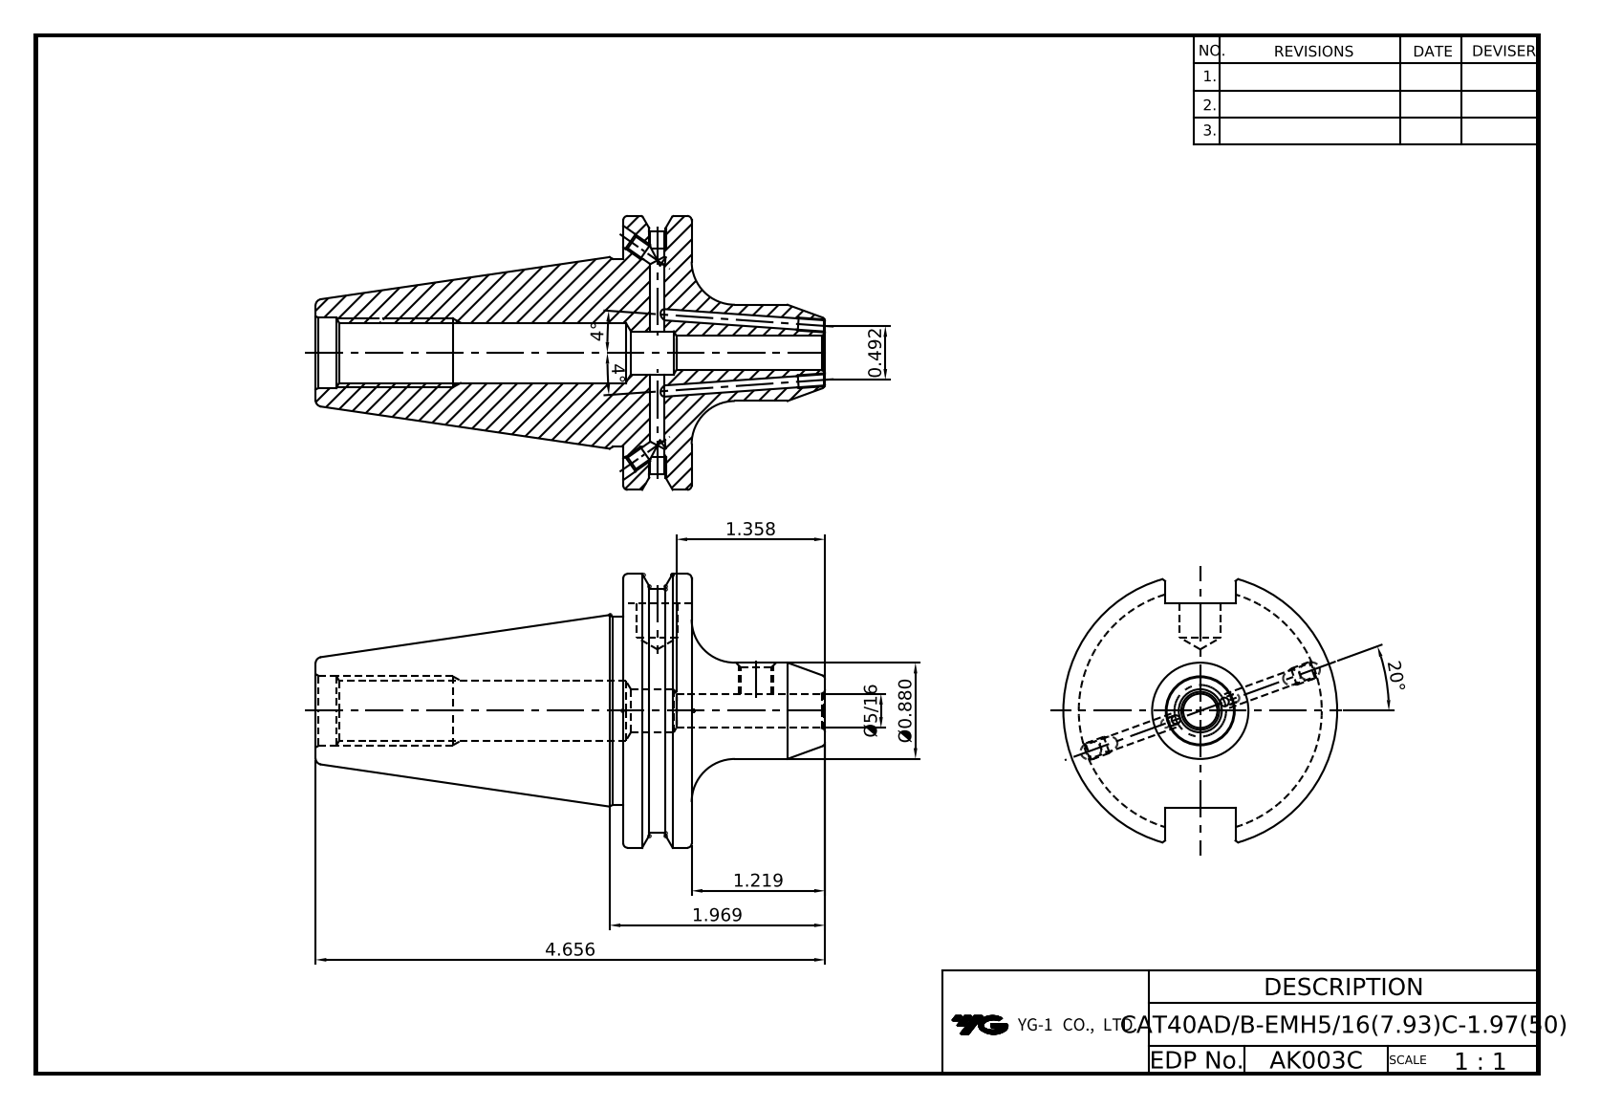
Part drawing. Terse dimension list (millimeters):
name: LO-CAT40ADB-EMH7.9375C-50
written by: Autodesk Inventor 2022 (AUTOMOTIVE_DESIGN)
unit: mm
bodies: 1 solid, 91 faces (36 planar, 31 cylindrical, 24 other)
size: 118.25 × 63.5 × 61.09
volume: 111 987 mm³; area: 23 968 mm²
holes: 4× ⌀3.24, 2× ⌀2.6, 2× ⌀4, 2× ⌀4.2, 1× ⌀6.78, 1× ⌀7.94, 1× ⌀9.53, 1× ⌀10, 1× ⌀13, 1× ⌀13.39, 1× ⌀16.3
bosses: 1× ⌀63.5, 1× ⌀43.6, 1× ⌀22.35
rounds: 1× R28.15
face distances: 15.88, 47.6, 16.38, 71.42, 87.3, 77.47, 6.05, 9.83, 81.3, 9.88
hole spacings: 22.87
